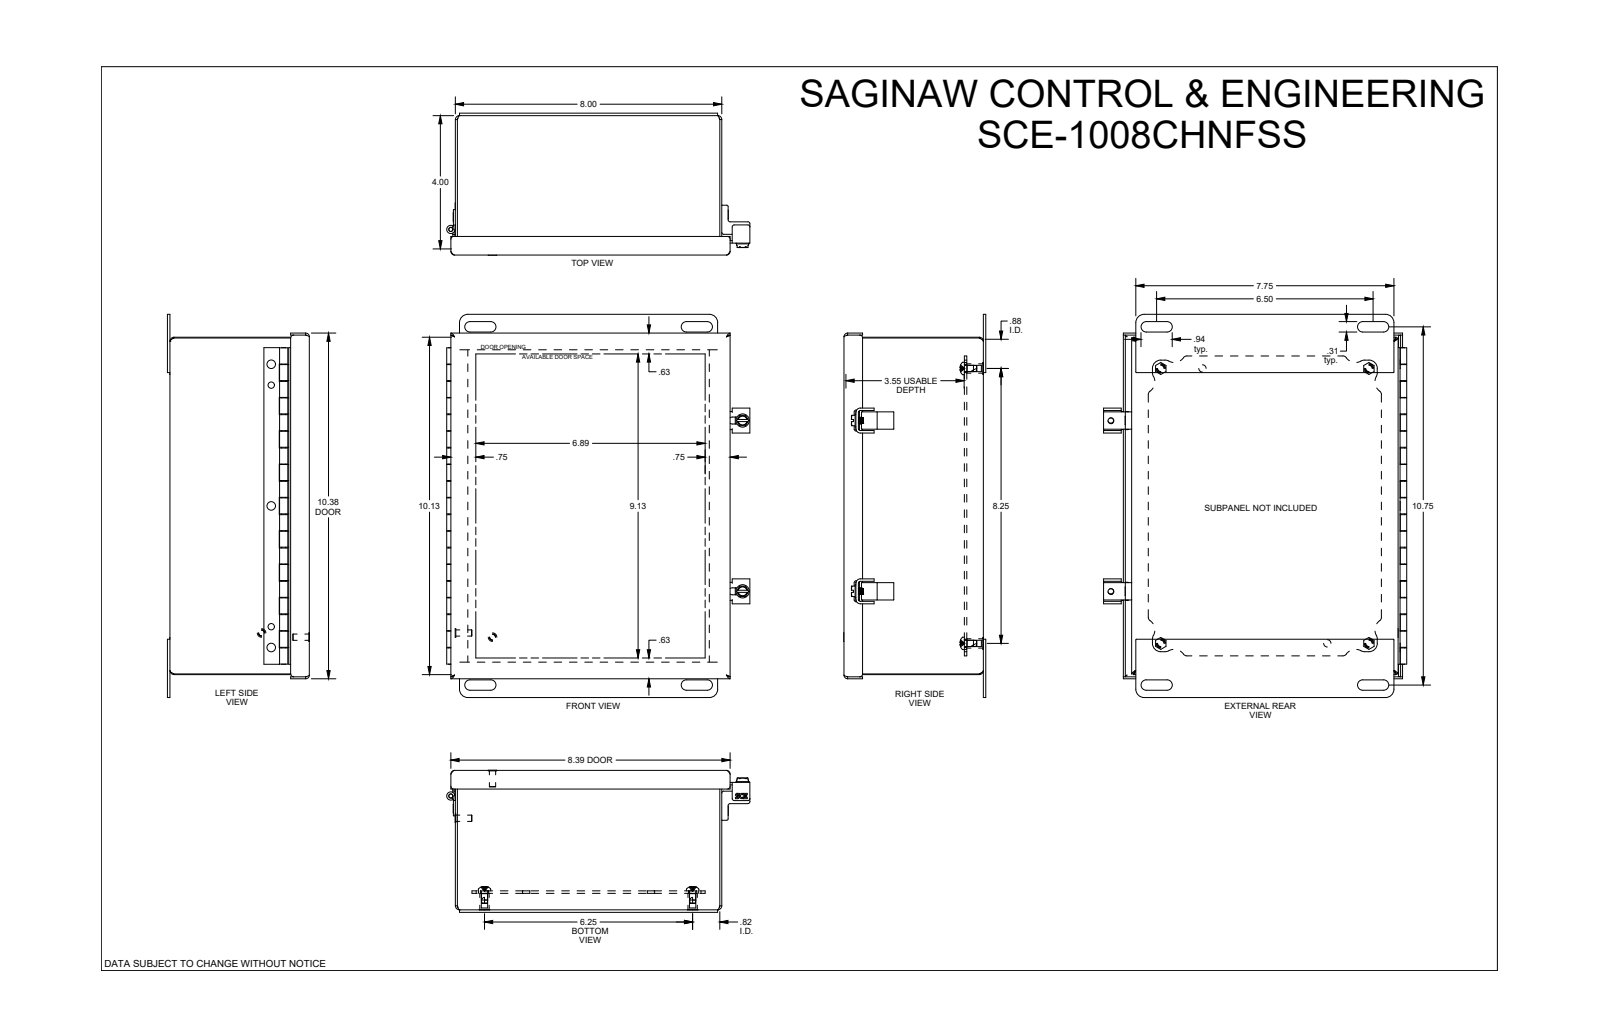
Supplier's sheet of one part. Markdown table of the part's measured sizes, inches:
| quantity | value |
| --- | --- |
| part name | SCE-1008CHNF |
| STEP written by | SolidWorks 2019 (AUTOMOTIVE_DESIGN) |
| units | inches |
| bodies | 37 solids, 1225 faces (537 planar, 341 cylindrical, 347 other) |
| overall size | 11.5 × 9.104 × 4.265 |
| volume | 30.92 in³ |
| surface area | 958.5 in² |
| round holes (diameter × count) | 0.19 × 9, 0.193 × 7, 0.25 × 4, 0.281 × 4, 0.156 × 2, 0.218 × 2, 0.266 × 2, 0.126 × 1, 0.187 × 1 |
| round bosses / shafts (diameter × count) | 0.188 × 11, 0.256 × 7, 0.373 × 4, 0.28 × 4, 0.396 × 2, 0.188 × 2, 0.246 × 1, 0.123 × 1 |
| partial cylindrical surfaces (radius × count) | 0.01 × 76, 0.06 × 33, 0.25 × 16, 0.05 × 8, 0.125 × 8, 0.156 × 8, 0.344 × 8, 0.027 × 6 |
| main face-to-face distances | 0.06, 4.125, 4.185, 4.065, 7.94, 0.075, 0.51, 0.435, 0.57, 3.555 |
| hole center spacings | 8.25, 6.25, 6.854, 8.344, 9.647, 10.236, 10.35, 1.065 |
